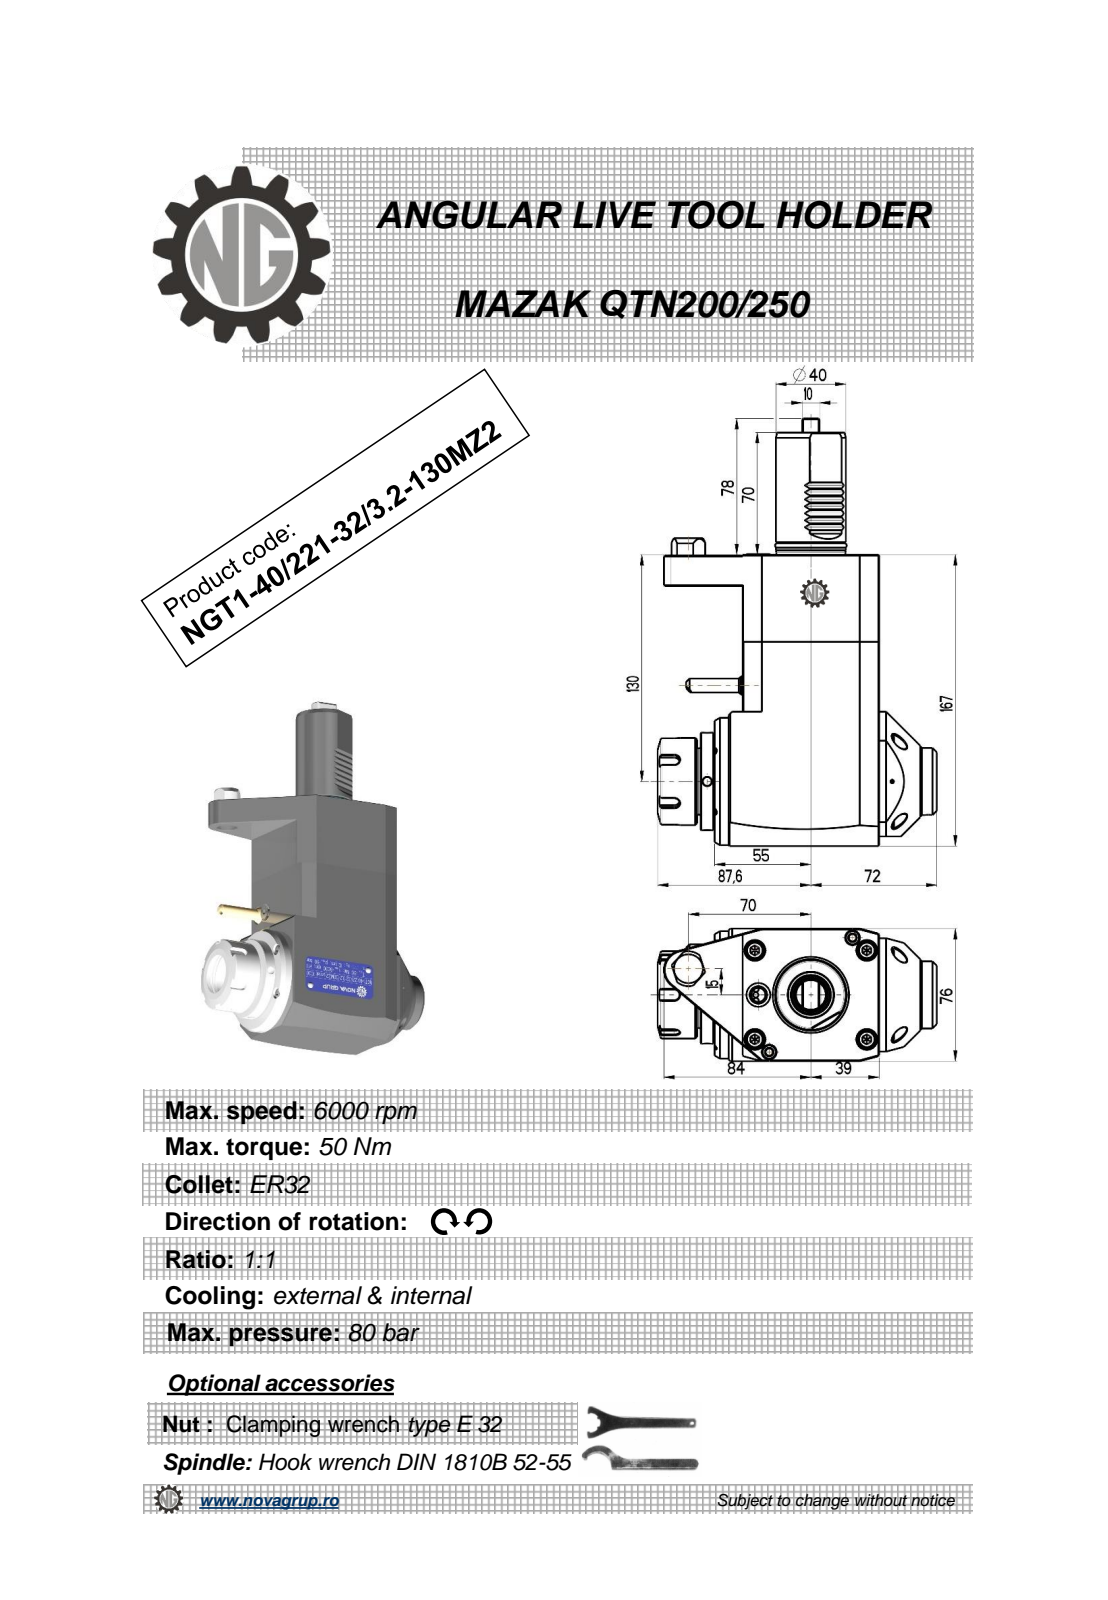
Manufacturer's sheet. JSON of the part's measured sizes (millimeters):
{"part_name": "NGT1_40_221_32_3_2_130MZ2", "step_written_by": "PRO/ENGINEER BY PARAMETRIC TECHNOLOGY CORPORATION, 2010280 (CONFIG_CONTROL_DESIGN)", "units": "millimeters", "bodies": {"solids": 1, "faces": 300, "planar": 137, "cylindrical": 76, "other": 87}, "overall_size": [245, 159.6, 76], "volume_mm3": 1312000, "surface_area_mm2": 93544, "round_holes": [[5, 3], [3, 1], [8, 1], [27, 1]], "round_bosses_or_shafts": [[73, 1], [56, 1], [50, 1], [43, 1], [40, 1], [39.4, 1], [38.5, 1], [36.2, 1]], "partial_cylinders_radius": [[0.3, 7], [0.2, 6], [3, 5], [0.8, 2], [300, 2], [9, 1], [10, 1], [11.35, 1]], "face_to_face_distances": [76, 78, 167, 8, 16, 94, 18, 87.92, 149, 86], "hole_center_spacings": [29.25, 60.42]}
